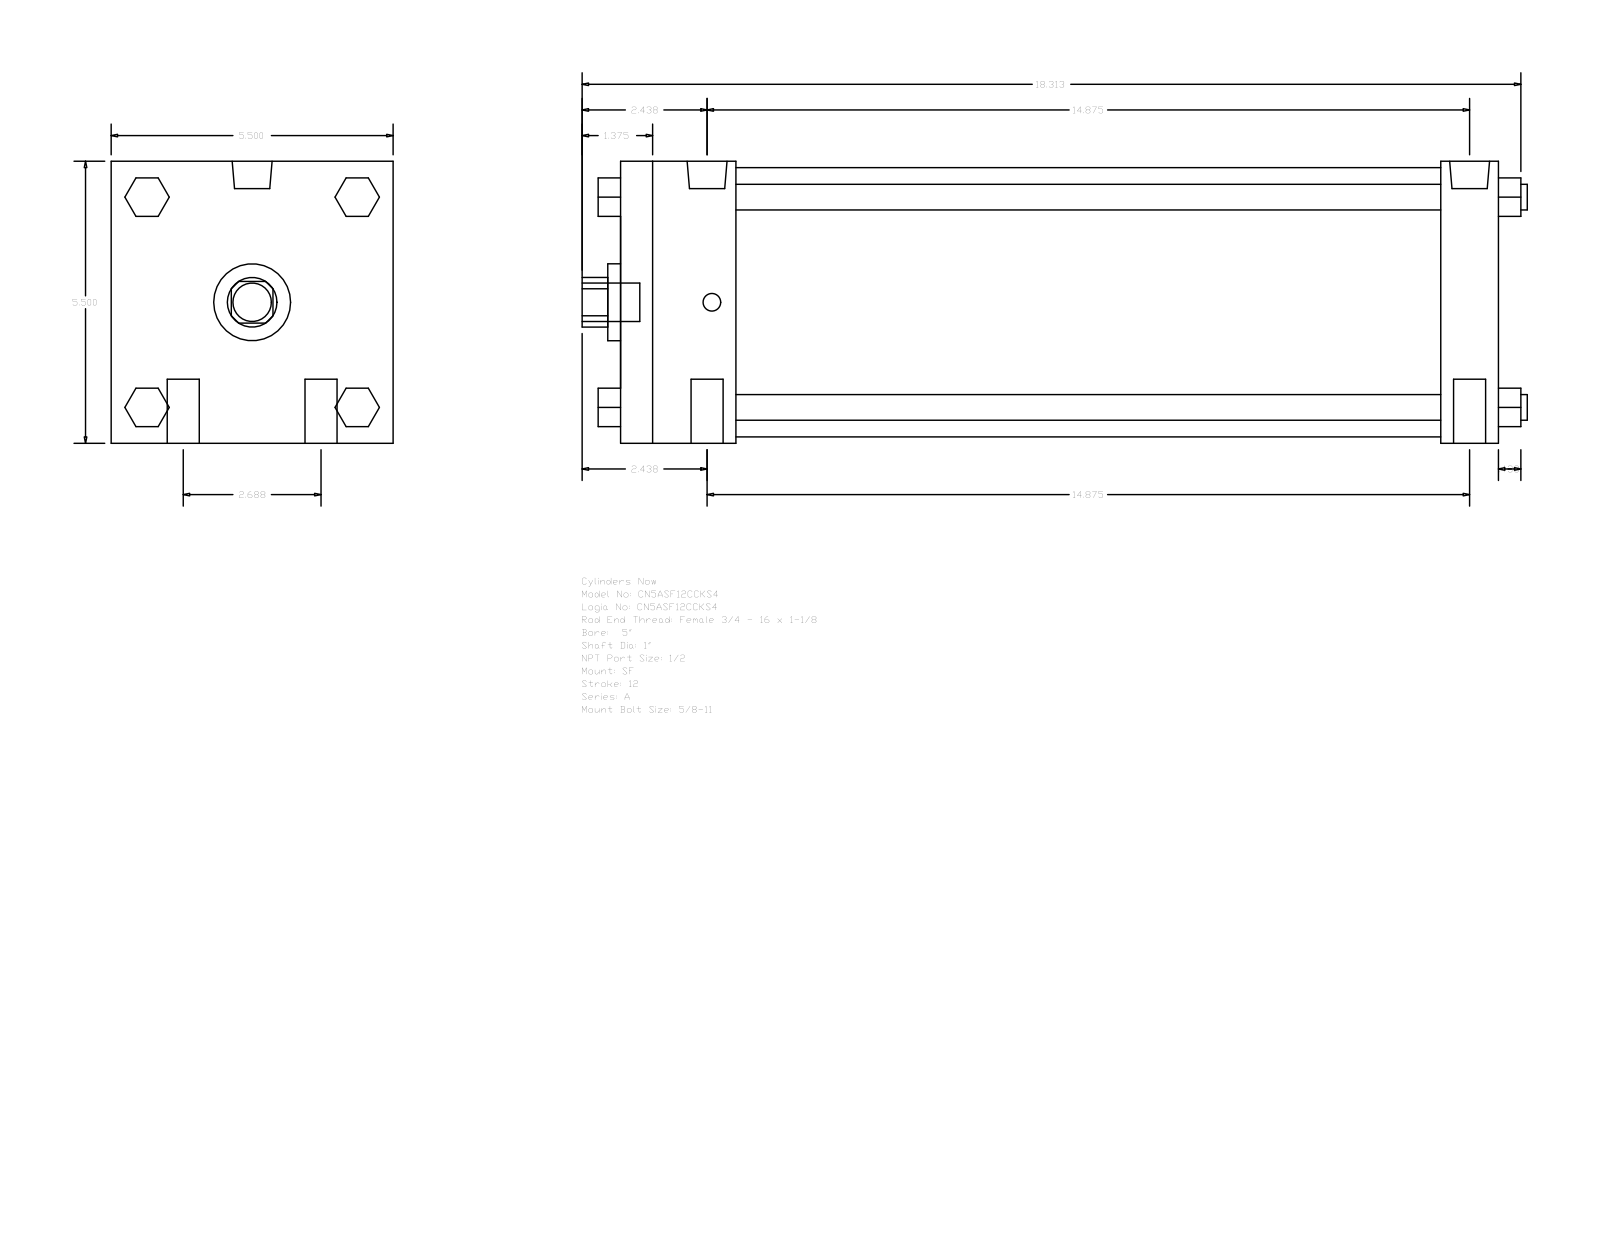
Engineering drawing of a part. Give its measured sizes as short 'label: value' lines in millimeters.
name: A_SF__0500_1
written by: GSSL Pune (CONFIG_CONTROL_DESIGN)
unit: mm
bodies: 0 solids, 124 faces (94 planar, 30 cylindrical, 0 other)
size: 468.31 × 139.7 × 139.7
holes: 1× ⌀25.4, 1× ⌀38.1, 1× ⌀133.35
bosses: 4× ⌀15.88, 4× ⌀12.7, 2× ⌀19.77, 2× ⌀8.73, 1× ⌀19.05
rounds: 1× R12.29
face distances: 139.7, 434.97, 28.57, 57.15, 406.4, 349.25, 377.82, 19.05, 52.07, 90.18
